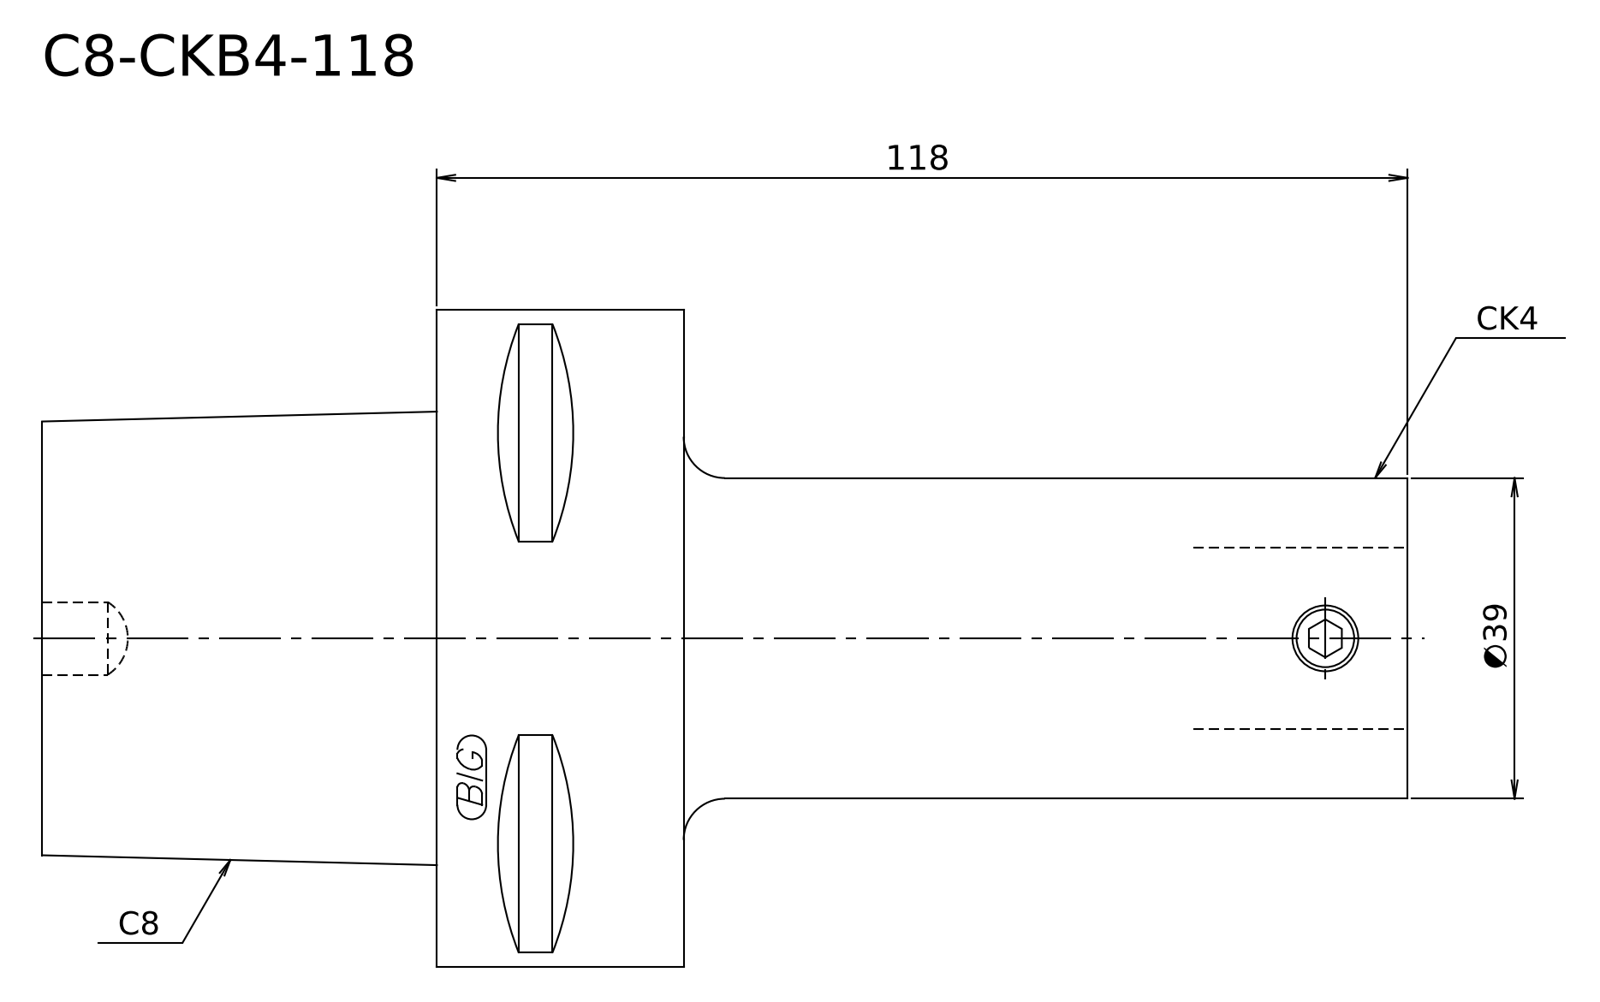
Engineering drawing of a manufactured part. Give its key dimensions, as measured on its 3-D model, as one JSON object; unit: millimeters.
{"step_written_by": "Kubotek KeyCreator V8.5.1 (14335) (CONFIG_CONTROL_DESIGN)", "units": "millimeters", "bodies": {"solids": 1, "faces": 8, "planar": 4, "cylindrical": 2, "other": 2}, "overall_size": [166, 79.98, 79.98], "volume_mm3": 363939, "surface_area_mm2": 35977, "round_bosses_or_shafts": [[79.98, 1], [39, 1]], "face_to_face_distances": [30, 78, 48, 88, 118, 166]}
